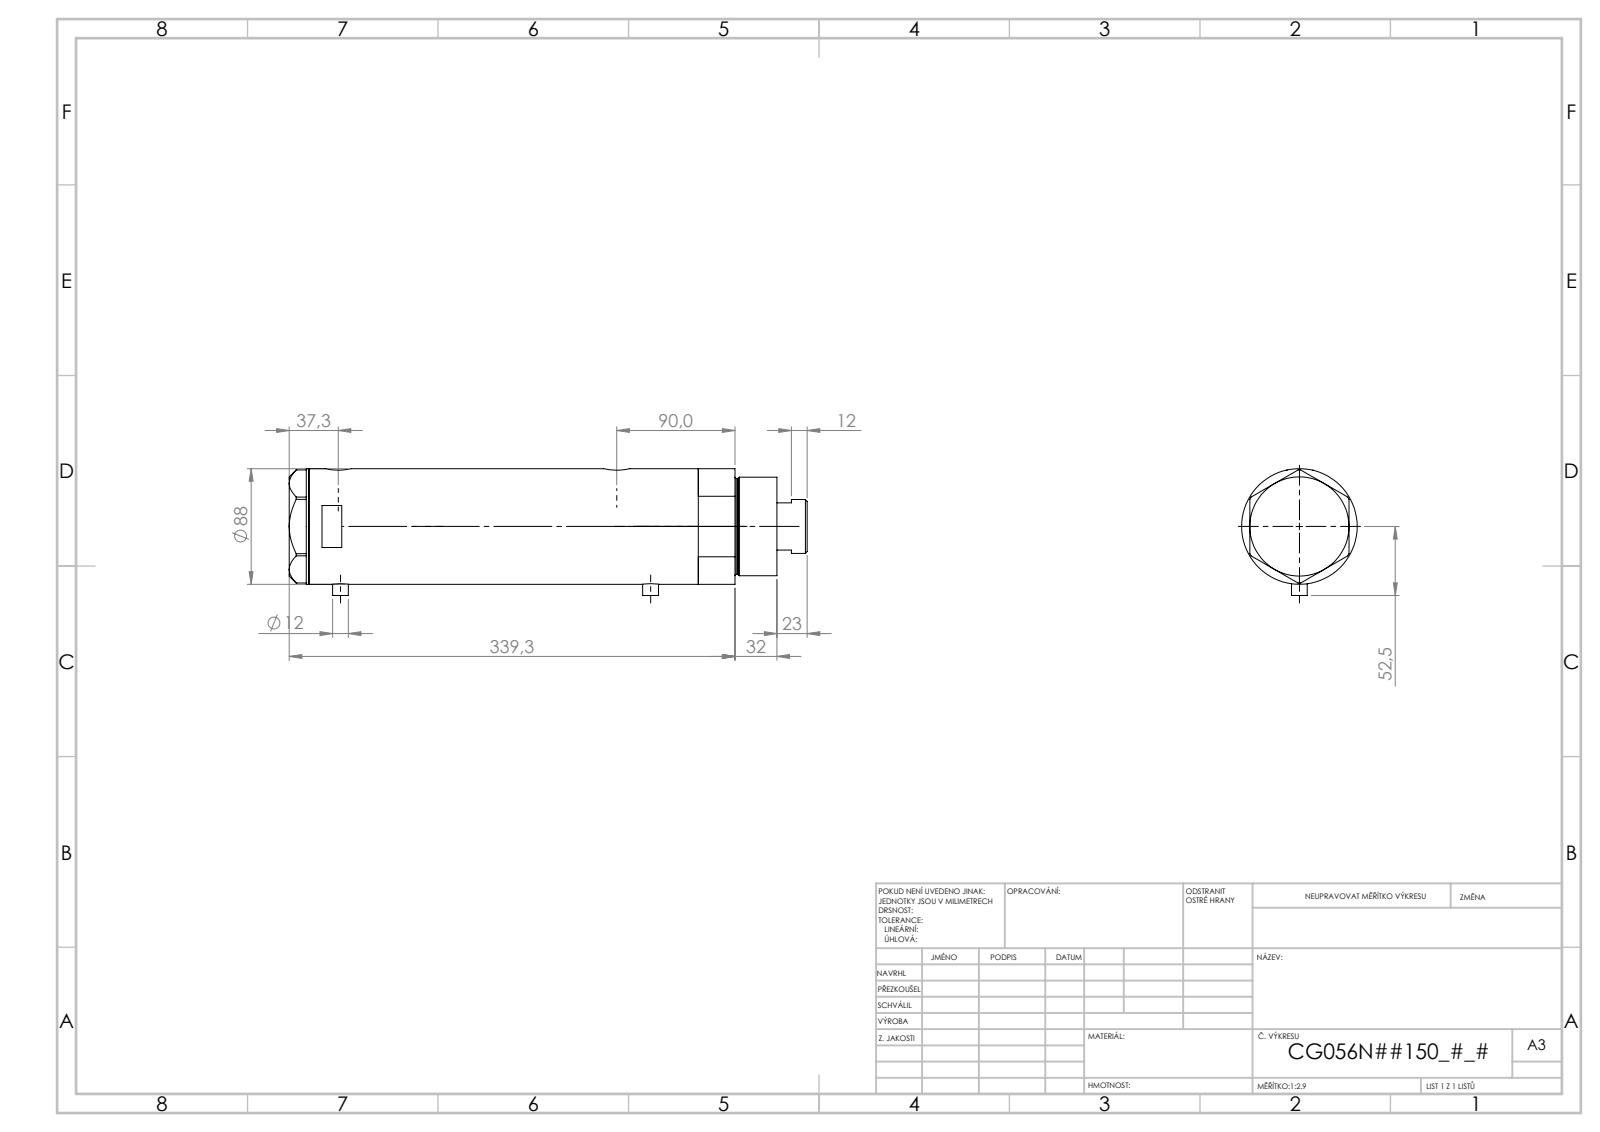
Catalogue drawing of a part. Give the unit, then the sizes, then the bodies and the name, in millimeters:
Units: millimetres
Overall size (bounding box): 374.47 × 89.1 × 88
Round holes (diameter × count): ⌀5 ×2, ⌀12.5 ×2, ⌀13.16 ×2, ⌀20 ×2, ⌀14.5 ×1, ⌀42 ×1, ⌀43.5 ×1, ⌀56 ×1, ⌀60 ×1, ⌀80 ×1
Round bosses / shafts (diameter × count): ⌀12 ×2, ⌀88 ×1, ⌀75 ×1, ⌀73 ×1, ⌀41 ×1
Main face-to-face distances: 224.4, 26, 198.4, 15, 41, 239.4, 336.47, 351.47, 310.47, 112.07
Hole centre spacings: 1.7, 25.8, 200.3, 202, 226.1, 227.8
Volume: 1 913 000 mm³ · Surface area: 267 910 mm²
Bodies: 4 solids, 126 faces (53 planar, 53 cylindrical, 20 other)
Part name (STEP PRODUCT): V270CG_FRONT; V270CG_BACK; V270CG_MIDDLE; V270CG_VC
STEP written by: SolidWorks 2019 (CONFIG_CONTROL_DESIGN)
